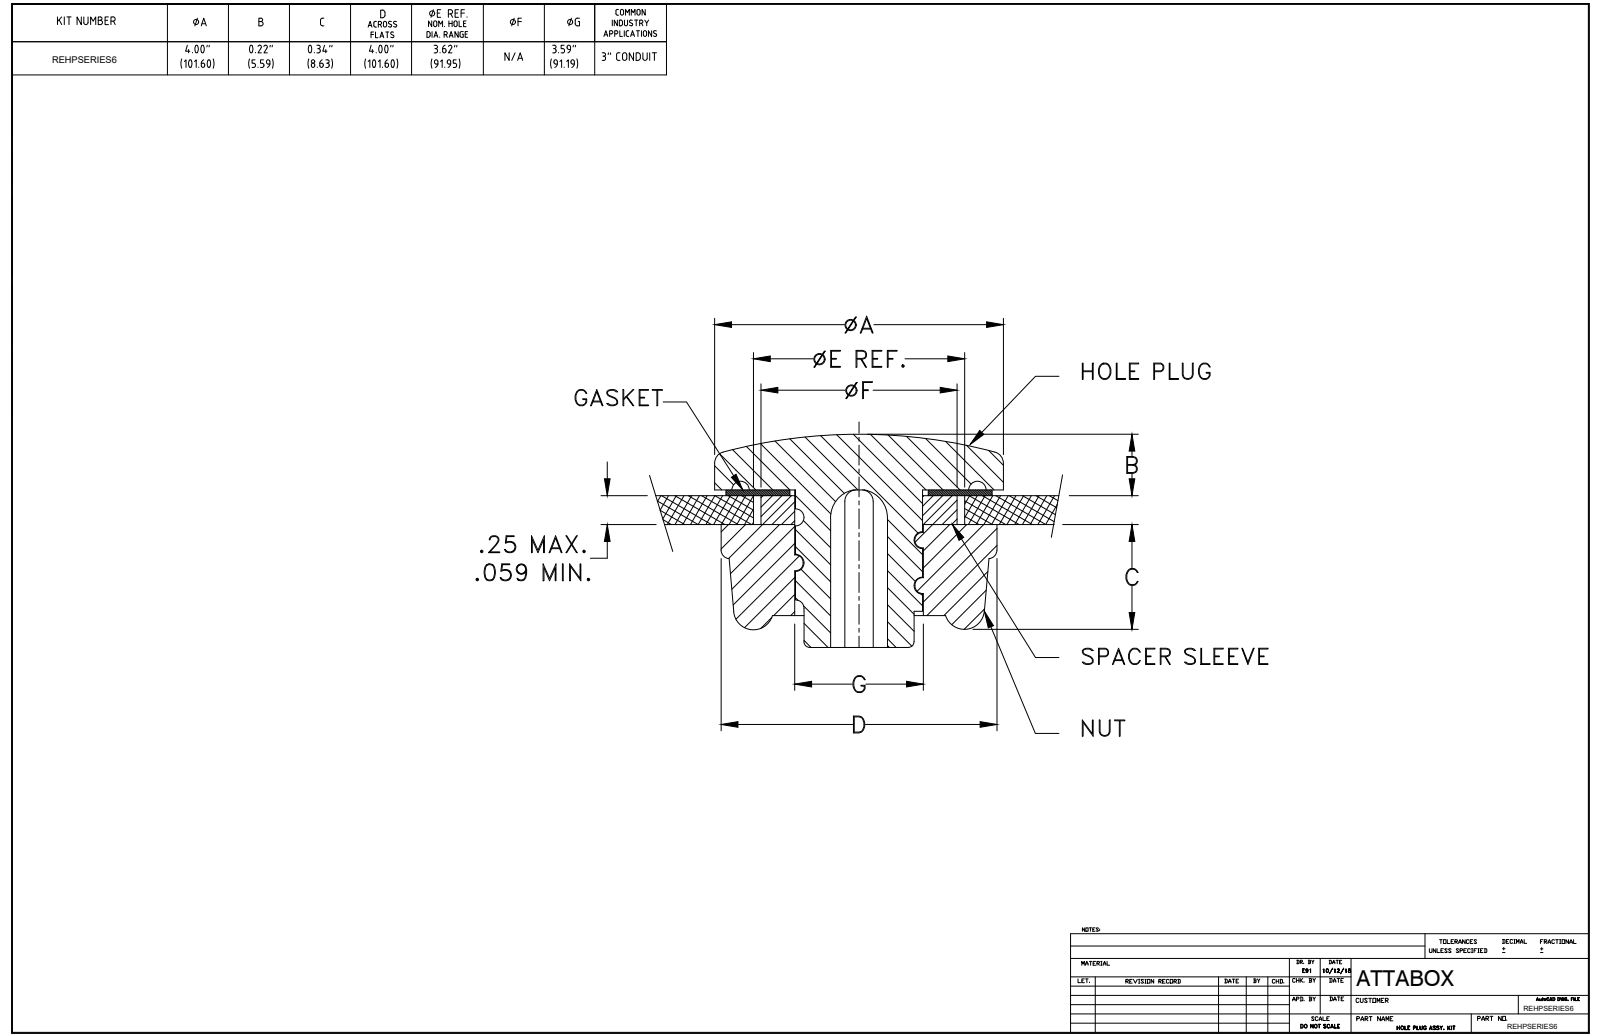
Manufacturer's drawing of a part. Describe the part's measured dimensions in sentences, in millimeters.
The part is named "HPSERIES6". Its 3-D file was written by "SolidWorks 2018 (AUTOMOTIVE_DESIGN)". It is 3 solids with 167 faces: 37 planar, 55 cylindrical and 75 other. Overall it measures 111.3 by 107.9 by 28.7 millimeters. Its volume is 134 300 cubic millimeters and its surface area 41 610 square millimeters. Round holes: 1 of diameter 91.2, 1 of diameter 91.4. Round bosses or shafts: 1 of diameter 101.6, 1 of diameter 101.1, 1 of diameter 98.6, 1 of diameter 89.7. Partial cylindrical surfaces (rounded edges, fillets, slot ends): 8 of radius 0.3, 8 of radius 1, 8 of radius 2, 6 of radius 0.8, 6 of radius 15, 4 of radius 0.2, 2 of radius 4.1. The main face-to-face distances are 6.2, 5.4, 0.8, 12.9, 18.3, 19.1, 66, 16, 3.2, 2.3.
